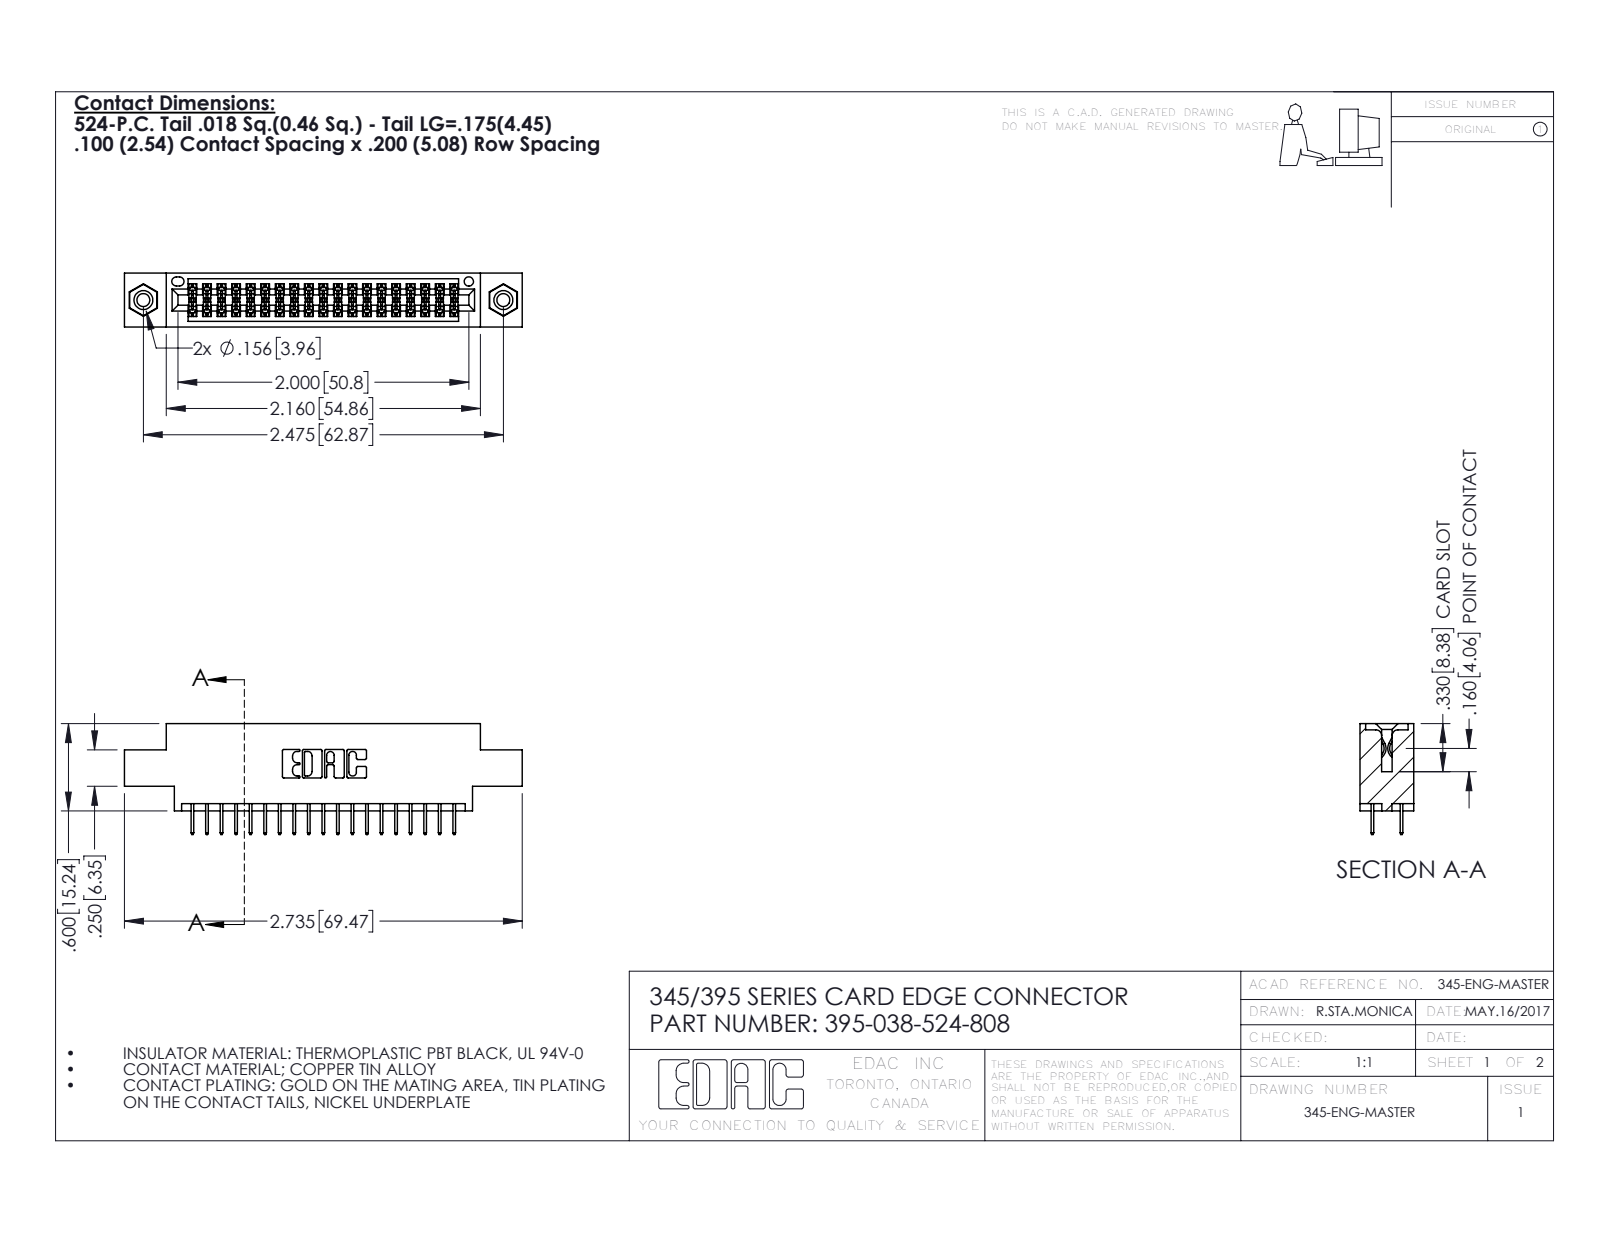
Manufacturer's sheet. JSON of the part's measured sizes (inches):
{"part_name": "345-250-001_345-250-003-102; 345 Part_0.170 Offset - 0.156 Dia-TI; 345-292-001_345-293-124; 395-038-524-808", "step_written_by": "SolidWorks 2016 (CONFIG_CONTROL_DESIGN)", "units": "inches", "bodies": {"solids": 41, "faces": 2242, "planar": 1598, "cylindrical": 628, "other": 16}, "overall_size": [2.735, 0.762, 0.37], "volume_in3": 0.388, "surface_area_in2": 13.88, "round_holes": [[0.089, 2], [0.125, 2], [0.156, 2], [0.064, 1]], "round_bosses_or_shafts": [[0.155, 2]], "partial_cylinders_radius": [[0.006, 57], [0.01, 22], [0.007, 6], [0.031, 6], [0.026, 3], [0.014, 2], [0.019, 2], [0.022, 2]], "face_to_face_distances": [0.072, 0.298, 0.37, 0.2, 0.098, 0.272, 0.025, 0.225, 0.175, 0.072], "hole_center_spacings": [0.27, 2.241, 2.475]}
